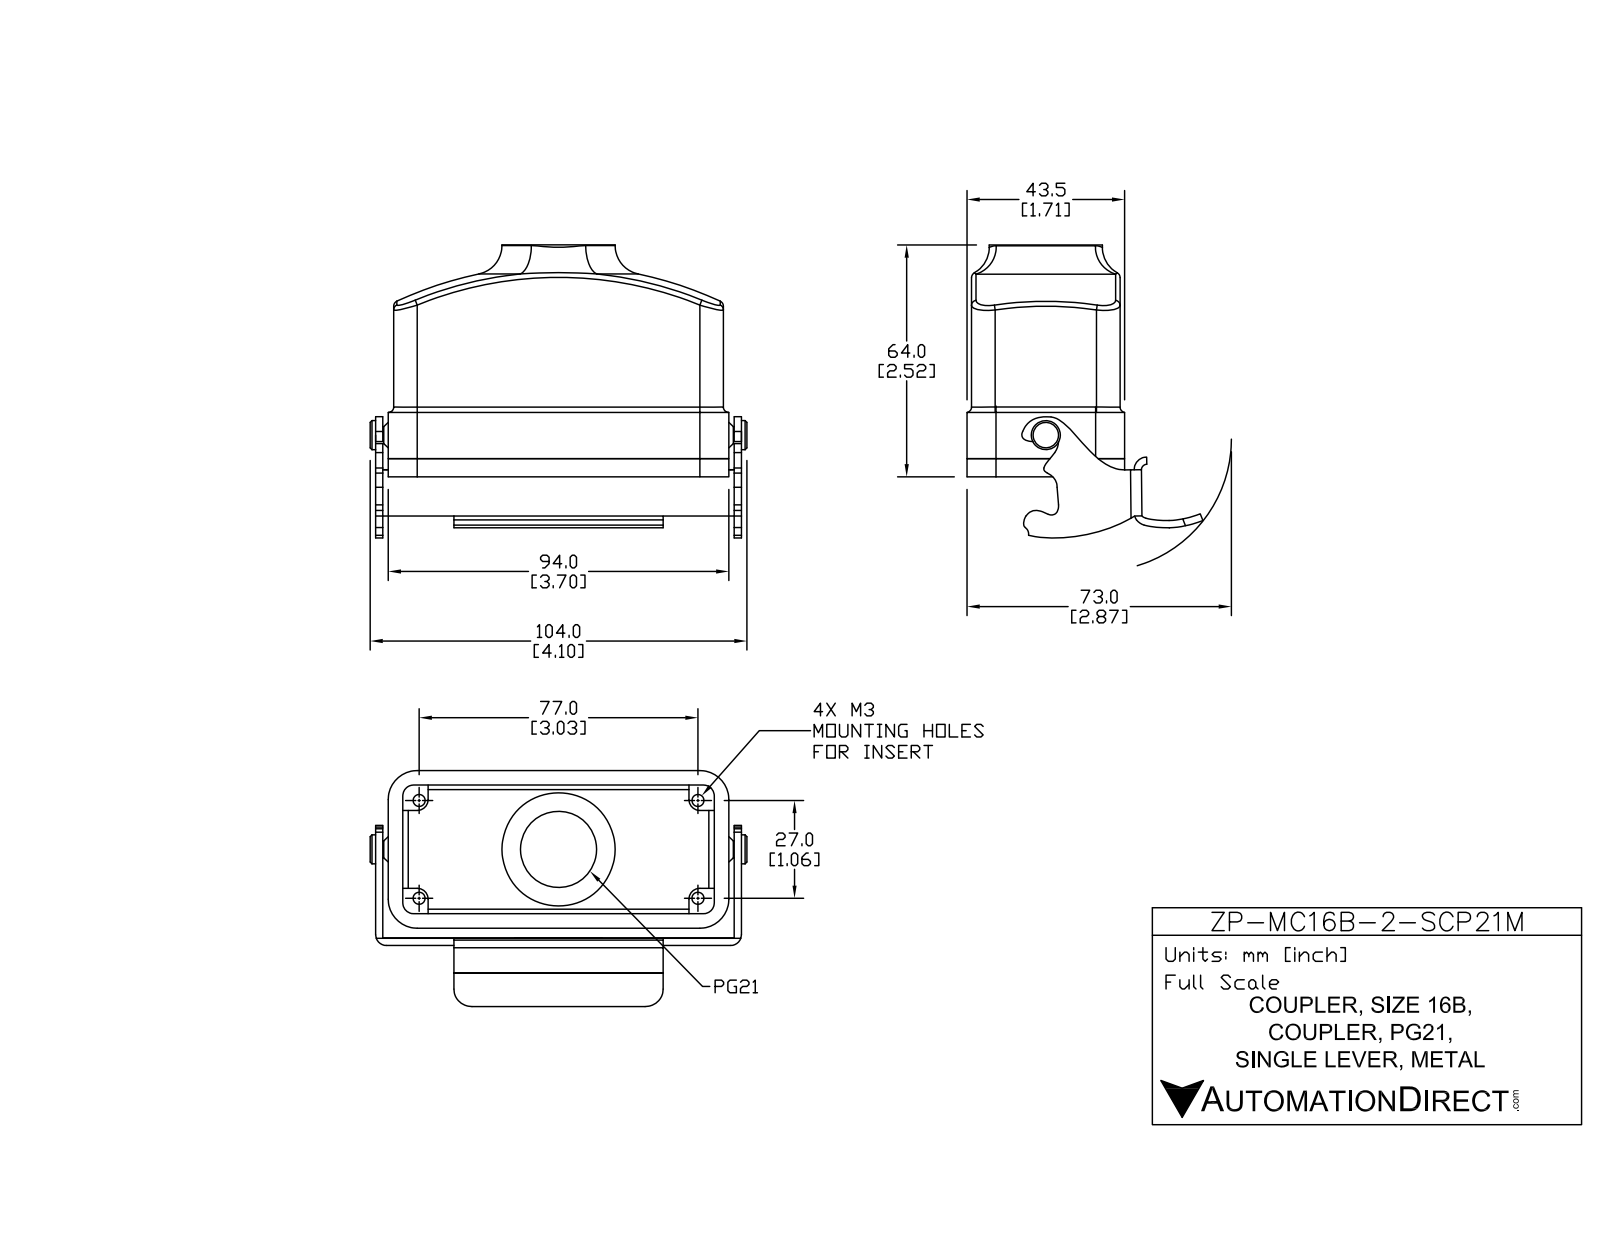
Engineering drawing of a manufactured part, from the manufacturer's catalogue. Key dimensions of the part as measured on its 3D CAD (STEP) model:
Part name (STEP PRODUCT): ZP-MC16B-2-SCP21M
STEP written by: SolidWorks 2011 (AUTOMOTIVE_DESIGN)
Units: millimetres
Bodies: 5 solids, 213 faces (82 planar, 104 cylindrical, 27 other)
Overall size (bounding box): 104 × 69.71 × 63.61
Volume: 70 294 mm³ · Surface area: 43 081 mm²
Round holes (diameter × count): ⌀3.3 ×4, ⌀21 ×1, ⌀26 ×1
Round bosses / shafts (diameter × count): ⌀31.25 ×1, ⌀8 ×1, ⌀4.67 ×1
Partial cylindrical surfaces — rounded edges, fillets, slot ends (radius × count): R0.5 ×13, R3 ×9, R1.5 ×4, R5.5 ×4, R6.5 ×4, R8 ×4, R2 ×3, R4 ×3
Main face-to-face distances: 4, 1.25, 38.25, 37, 5.25, 2.75, 42.25, 41, 39.5, 34.25
Hole centre spacings: 40.95, 26.5, 77.5, 81.91
